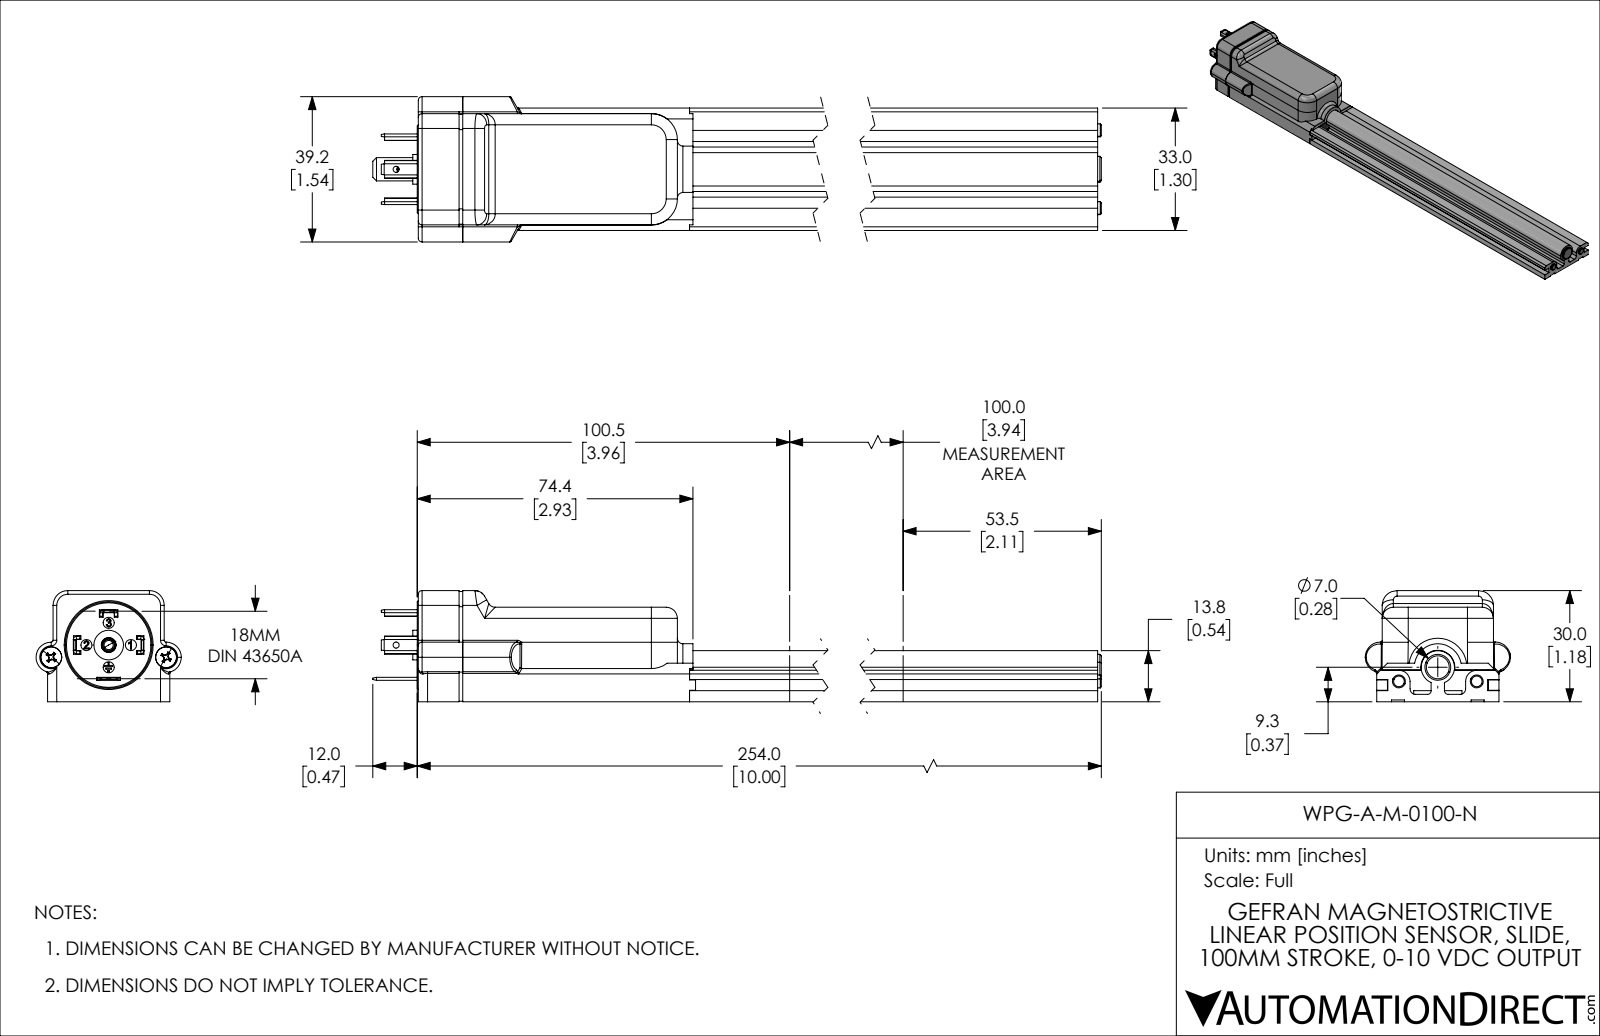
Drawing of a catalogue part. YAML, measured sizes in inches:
part_name: "WPG-A-M-0100-N"
step_written_by: "SolidWorks 2021 (CONFIG_CONTROL_DESIGN)"
units: inches
bodies: {solids: 15, faces: 589, planar: 371, cylindrical: 139, other: 79}
overall_size: [10.472, 1.543, 1.181]
volume: 6.208
surface_area: 63.42
round_holes:
  - {diameter: 0.118, count: 5}
  - {diameter: 0.059, count: 2}
  - {diameter: 0.065, count: 2}
  - {diameter: 0.126, count: 2}
  - {diameter: 0.224, count: 2}
  - {diameter: 0.063, count: 1}
  - {diameter: 0.098, count: 1}
  - {diameter: 0.157, count: 1}
round_bosses_or_shafts:
  - {diameter: 0.22, count: 2}
  - {diameter: 0.138, count: 2}
  - {diameter: 0.112, count: 2}
  - {diameter: 0.354, count: 1}
  - {diameter: 0.315, count: 1}
  - {diameter: 0.276, count: 1}
  - {diameter: 0.209, count: 1}
  - {diameter: 0.155, count: 1}
partial_cylinders:
  - {radius: 0.02, count: 8}
  - {radius: 0.118, count: 8}
  - {radius: 0.033, count: 6}
  - {radius: 0.039, count: 5}
  - {radius: 0.031, count: 4}
  - {radius: 0.059, count: 4}
  - {radius: 0.161, count: 4}
  - {radius: 0.276, count: 4}
face_to_face_distances: [0.039, 0.118, 0.059, 0.098, 0.217, 0.236, 0.886, 1.181, 0.335, 1.299]
hole_center_spacings: [0.236, 0.334, 0.396, 0.472, 0.484, 0.619, 0.624, 0.712]
